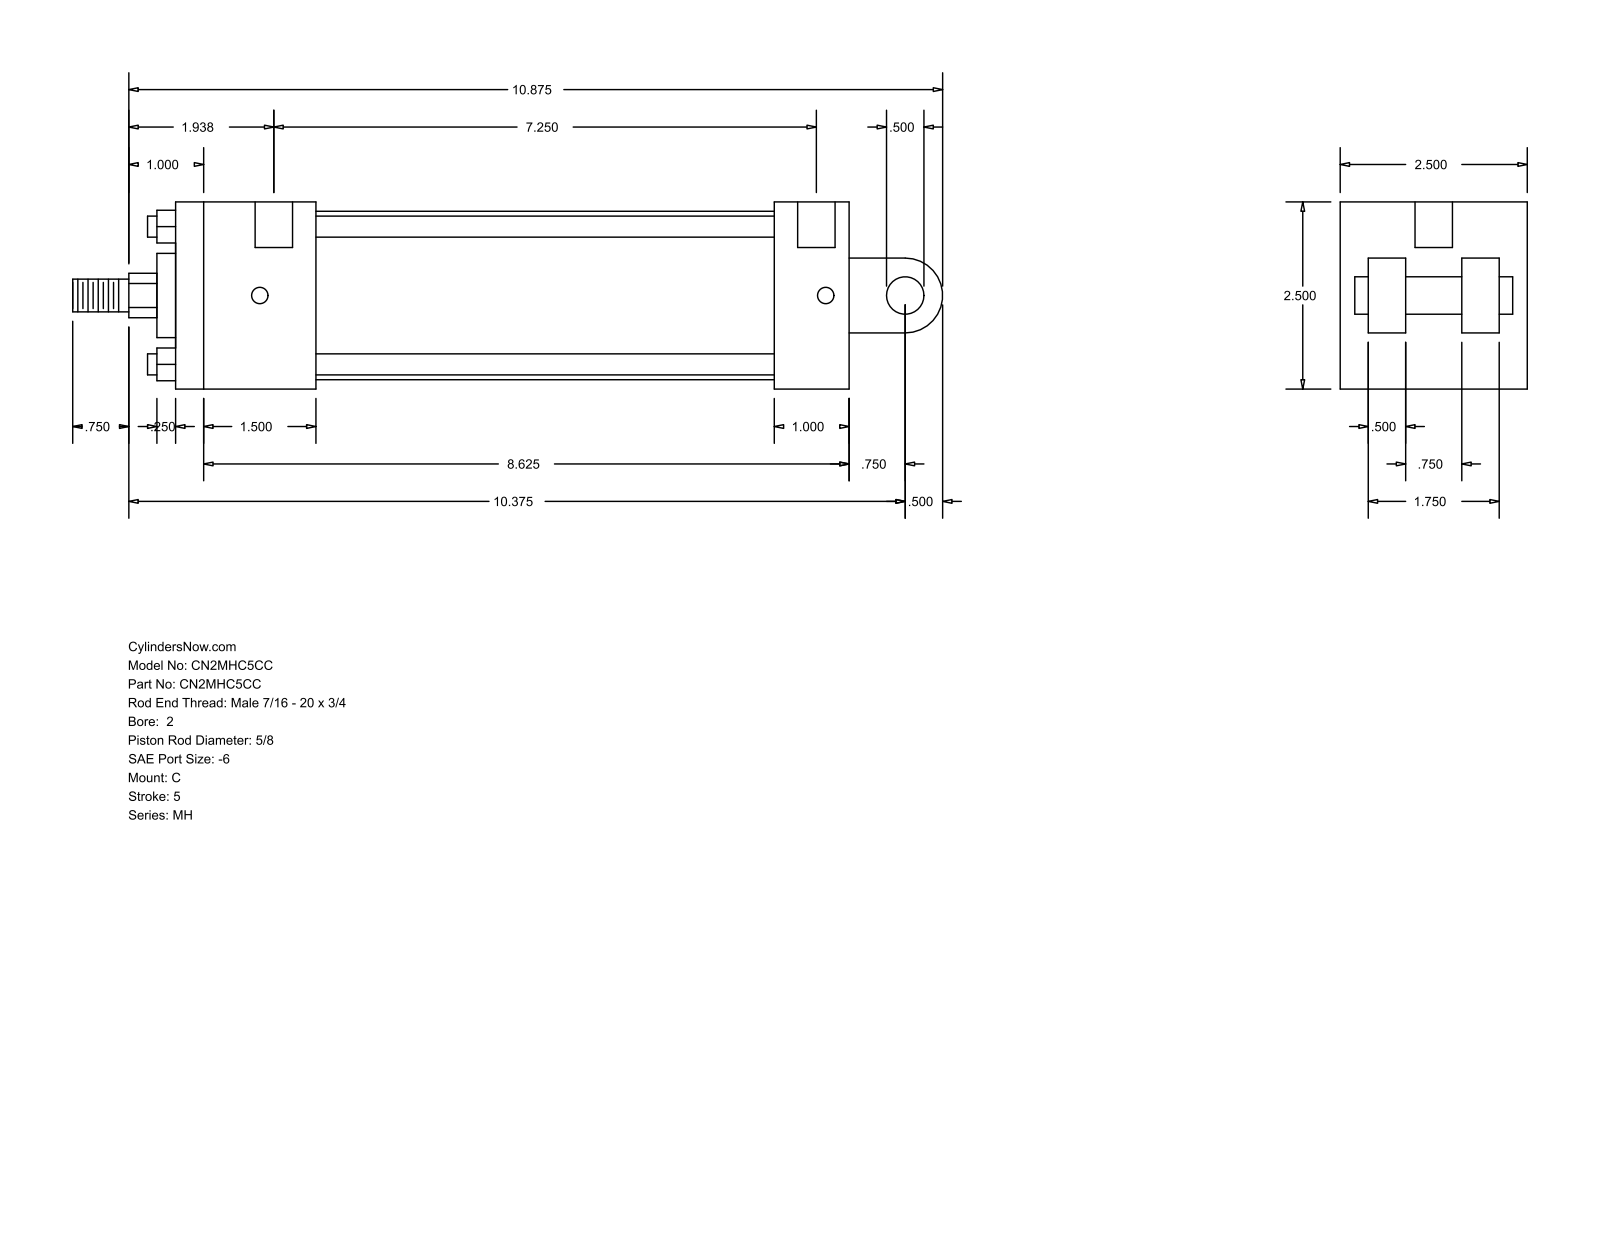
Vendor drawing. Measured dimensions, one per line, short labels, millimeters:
name: MH_C__0200_0.625
written by: GSSL Pune (CONFIG_CONTROL_DESIGN)
unit: mm
bodies: 0 solids, 99 faces (70 planar, 29 cylindrical, 0 other)
size: 295.27 × 63.5 × 63.5
holes: 4× ⌀5.56, 2× ⌀12.7
bosses: 4× ⌀7.14, 1× ⌀57.15, 1× ⌀28.57, 1× ⌀15.88, 1× ⌀12.7, 1× ⌀11.11
rounds: 1× R7.54, 1× R12.7
face distances: 63.5, 228.59, 25.4, 12.7, 47.62, 203.19, 155.57, 180.97, 19.05, 22.22
hole spacings: 192.09, 3.18, 4.76, 184.15, 187.33, 188.91
